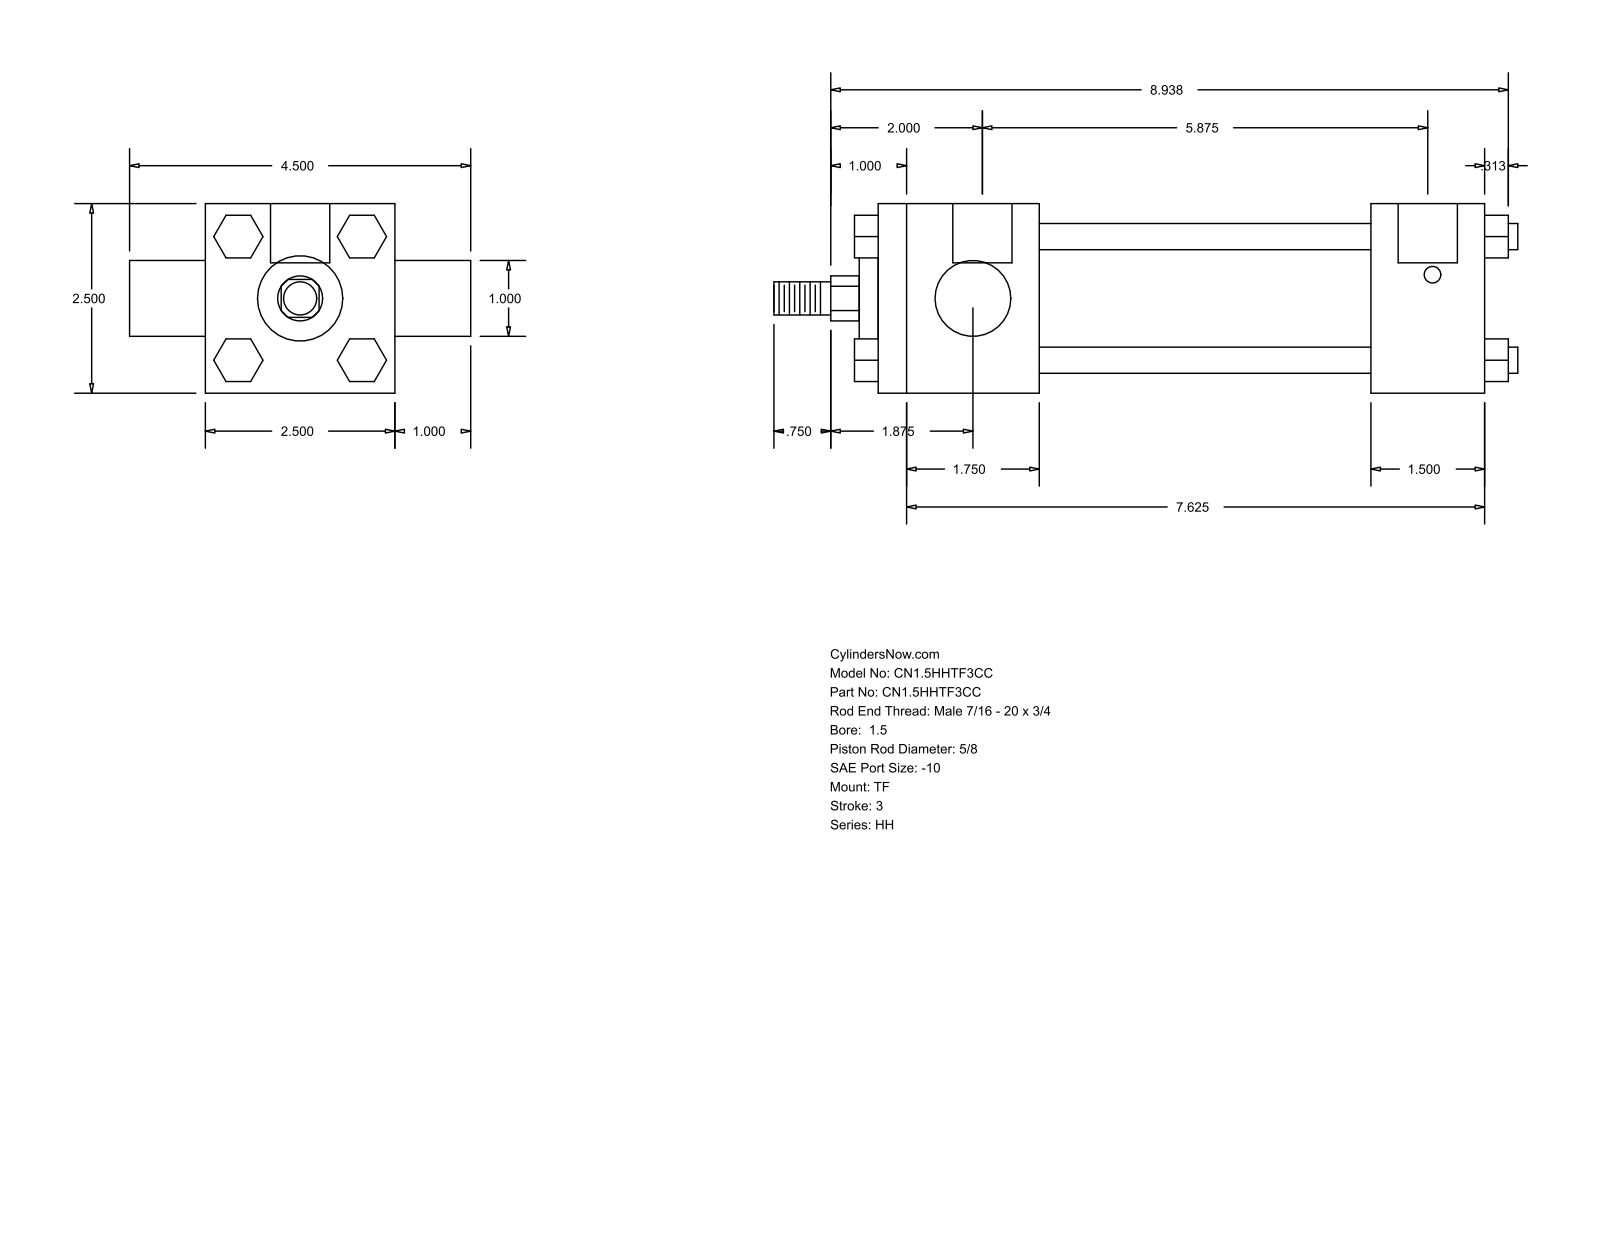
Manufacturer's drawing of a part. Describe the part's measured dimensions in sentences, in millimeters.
The part is named "HH_TF__0150_0.625". Its 3-D file was written by "GSSL Pune (CONFIG_CONTROL_DESIGN)". It is 0 solids with 120 faces: 92 planar, 28 cylindrical and 0 other. Overall it measures 249.24 by 114.3 by 63.5 millimeters. Round holes: 3 of diameter 5.56, 2 of diameter 19.84. Round bosses or shafts: 4 of diameter 8.76, 1 of diameter 44.45, 1 of diameter 28.57, 1 of diameter 25.4, 1 of diameter 15.88, 1 of diameter 11.11. Partial cylindrical surfaces (rounded edges, fillets, slot ends): 1 of radius 7.54. The main face-to-face distances are 63.5, 203.19, 38.1, 53.97, 149.22, 165.09, 111.12, 25.4, 88.9, 20.7. The hole center spacings are 1.58, 1.59, 149.23, 150.81, 150.82, 152.4.
